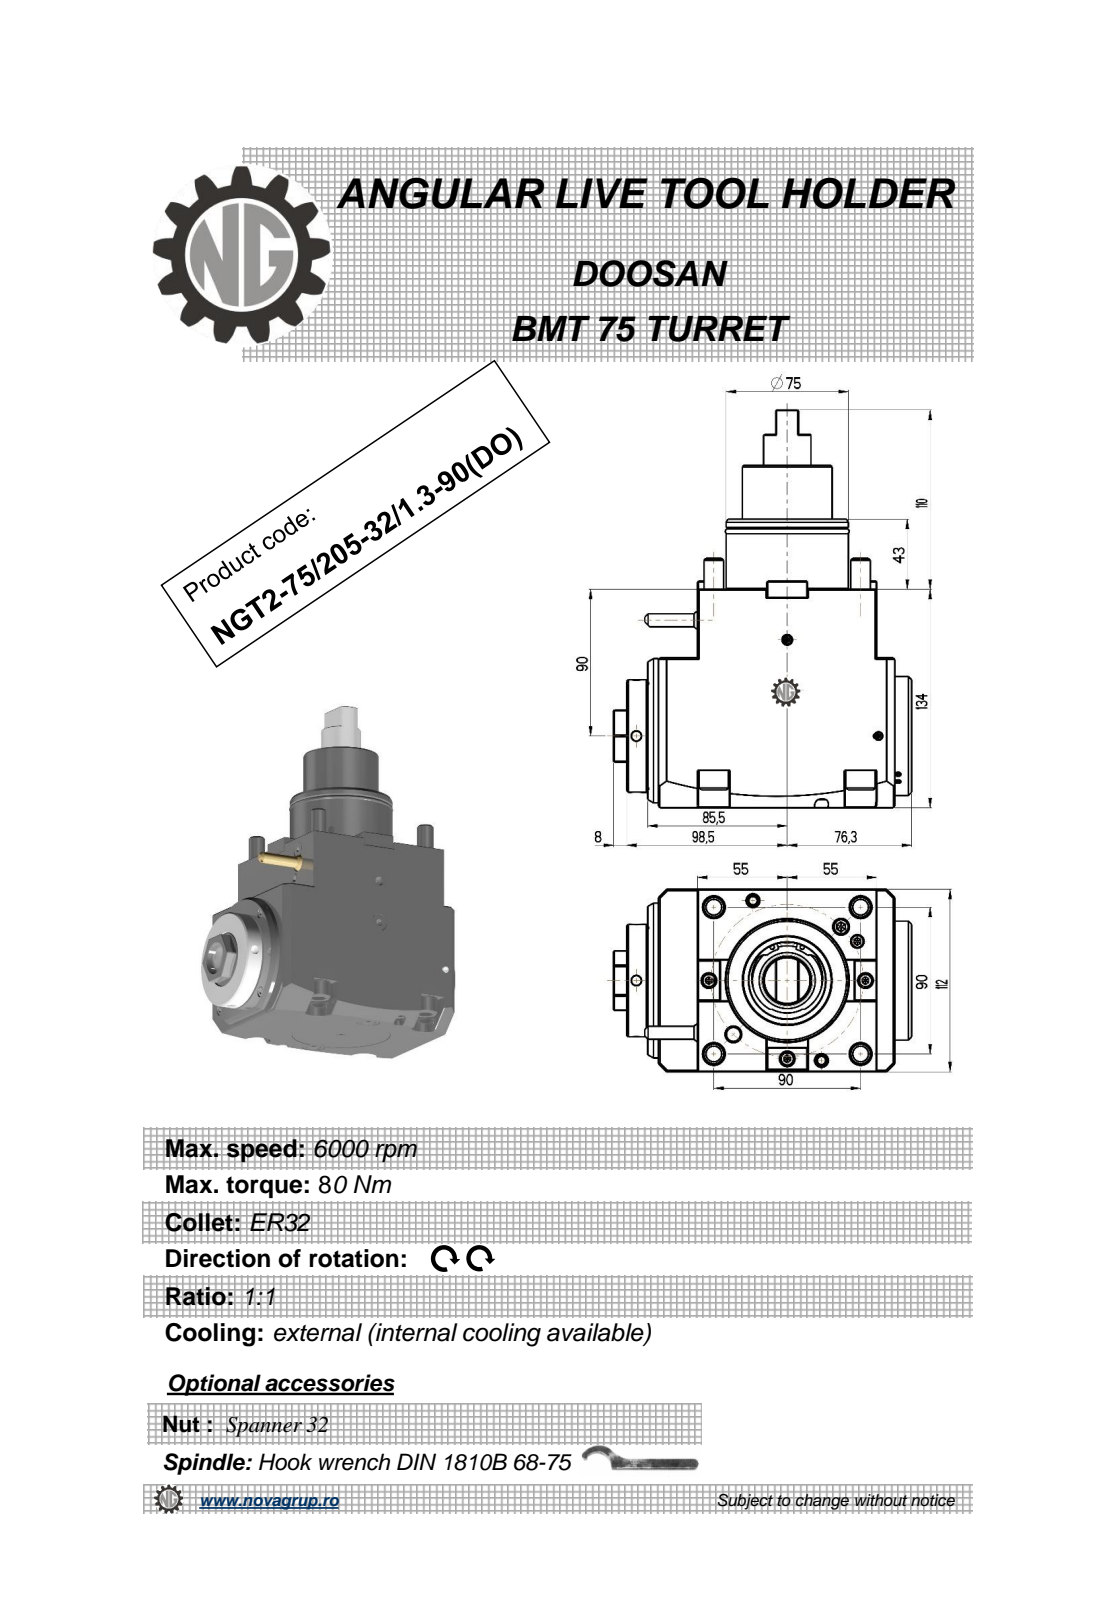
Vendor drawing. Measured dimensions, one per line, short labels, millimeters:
name: NGT2_75_205_32_1_3_90_DO
written by: PRO/ENGINEER BY PARAMETRIC TECHNOLOGY CORPORATION, 2010280 (CONFIG_CONTROL_DESIGN)
unit: mm
bodies: 2 solids, 292 faces (146 planar, 69 cylindrical, 77 other)
size: 244 × 182.8 × 112
volume: 2 411 000 mm³; area: 138 182 mm²
holes: 2× ⌀6, 2× ⌀8.5, 1× ⌀3, 1× ⌀5, 1× ⌀23
bosses: 4× ⌀18, 4× ⌀12, 1× ⌀95, 1× ⌀75, 1× ⌀74, 1× ⌀73, 1× ⌀70, 1× ⌀69
rounds: 4× R9.5, 2× R0.8, 2× R350
face distances: 112, 134, 11, 110, 121, 42, 92, 43.5, 131.3, 21.3
hole spacings: 68.04, 77.88, 93.34, 129.77
